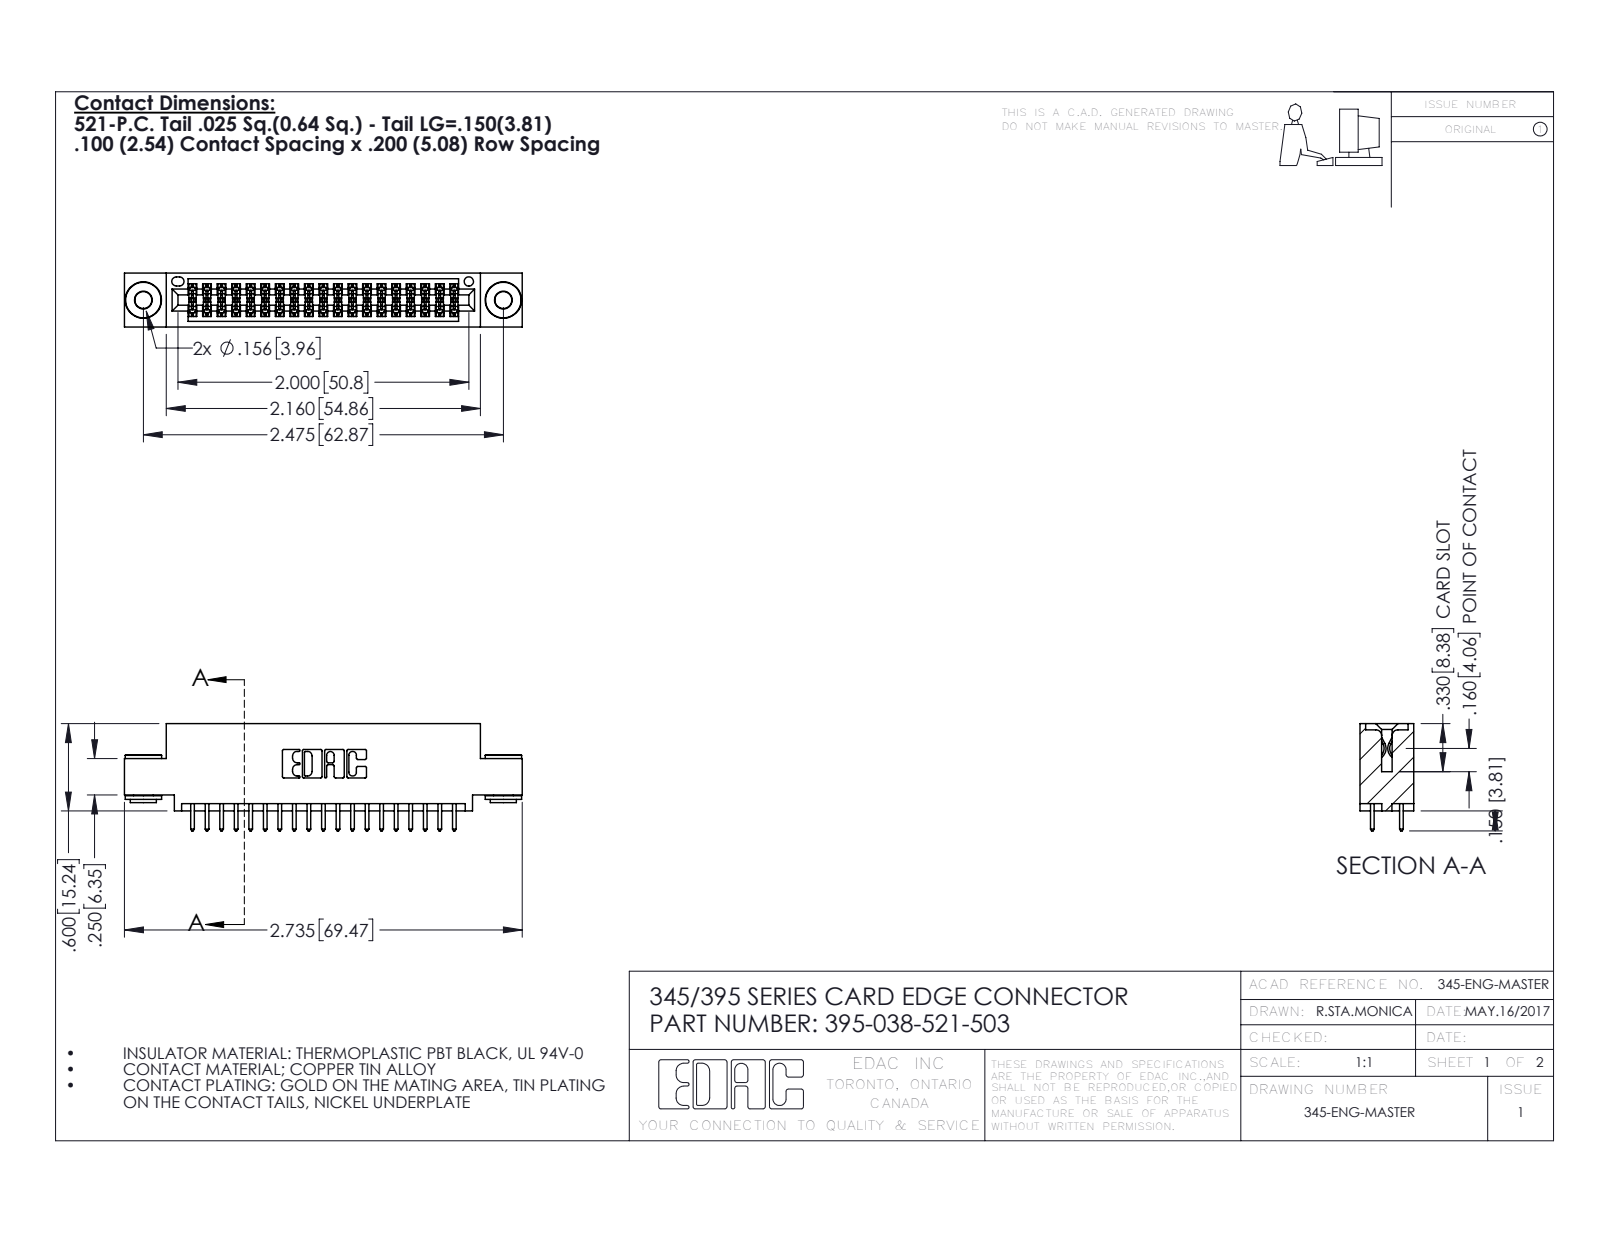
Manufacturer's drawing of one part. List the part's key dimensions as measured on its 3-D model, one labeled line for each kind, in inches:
Part name (STEP PRODUCT): 395-038-521-503; 345 Part_0.110 Offset - 0.156 Dia-TH; 345-292-001_345-293-121; 345-250-002_345-250-002-102
STEP written by: SolidWorks 2016 (CONFIG_CONTROL_DESIGN)
Units: inches
Bodies: 41 solids, 2068 faces (1348 planar, 712 cylindrical, 8 other)
Overall size (bounding box): 2.735 × 0.737 × 0.37
Volume: 0.395 in³ · Surface area: 14.43 in²
Round holes (diameter × count): ⌀0.116 ×2, ⌀0.156 ×2, ⌀0.064 ×1
Round bosses / shafts (diameter × count): ⌀0.25 ×2, ⌀0.18 ×2, ⌀0.136 ×2
Partial cylindrical surfaces — rounded edges, fillets, slot ends (radius × count): R0.006 ×57, R0.01 ×38, R0.01 ×22, R0.007 ×6, R0.031 ×6, R0.026 ×3, R0.014 ×2, R0.019 ×2
Main face-to-face distances: 0.072, 0.298, 0.2, 0.37, 0.025, 0.098, 0.272, 0.225, 0.175, 0.149
Hole centre spacings: 0.27, 2.241, 2.475
